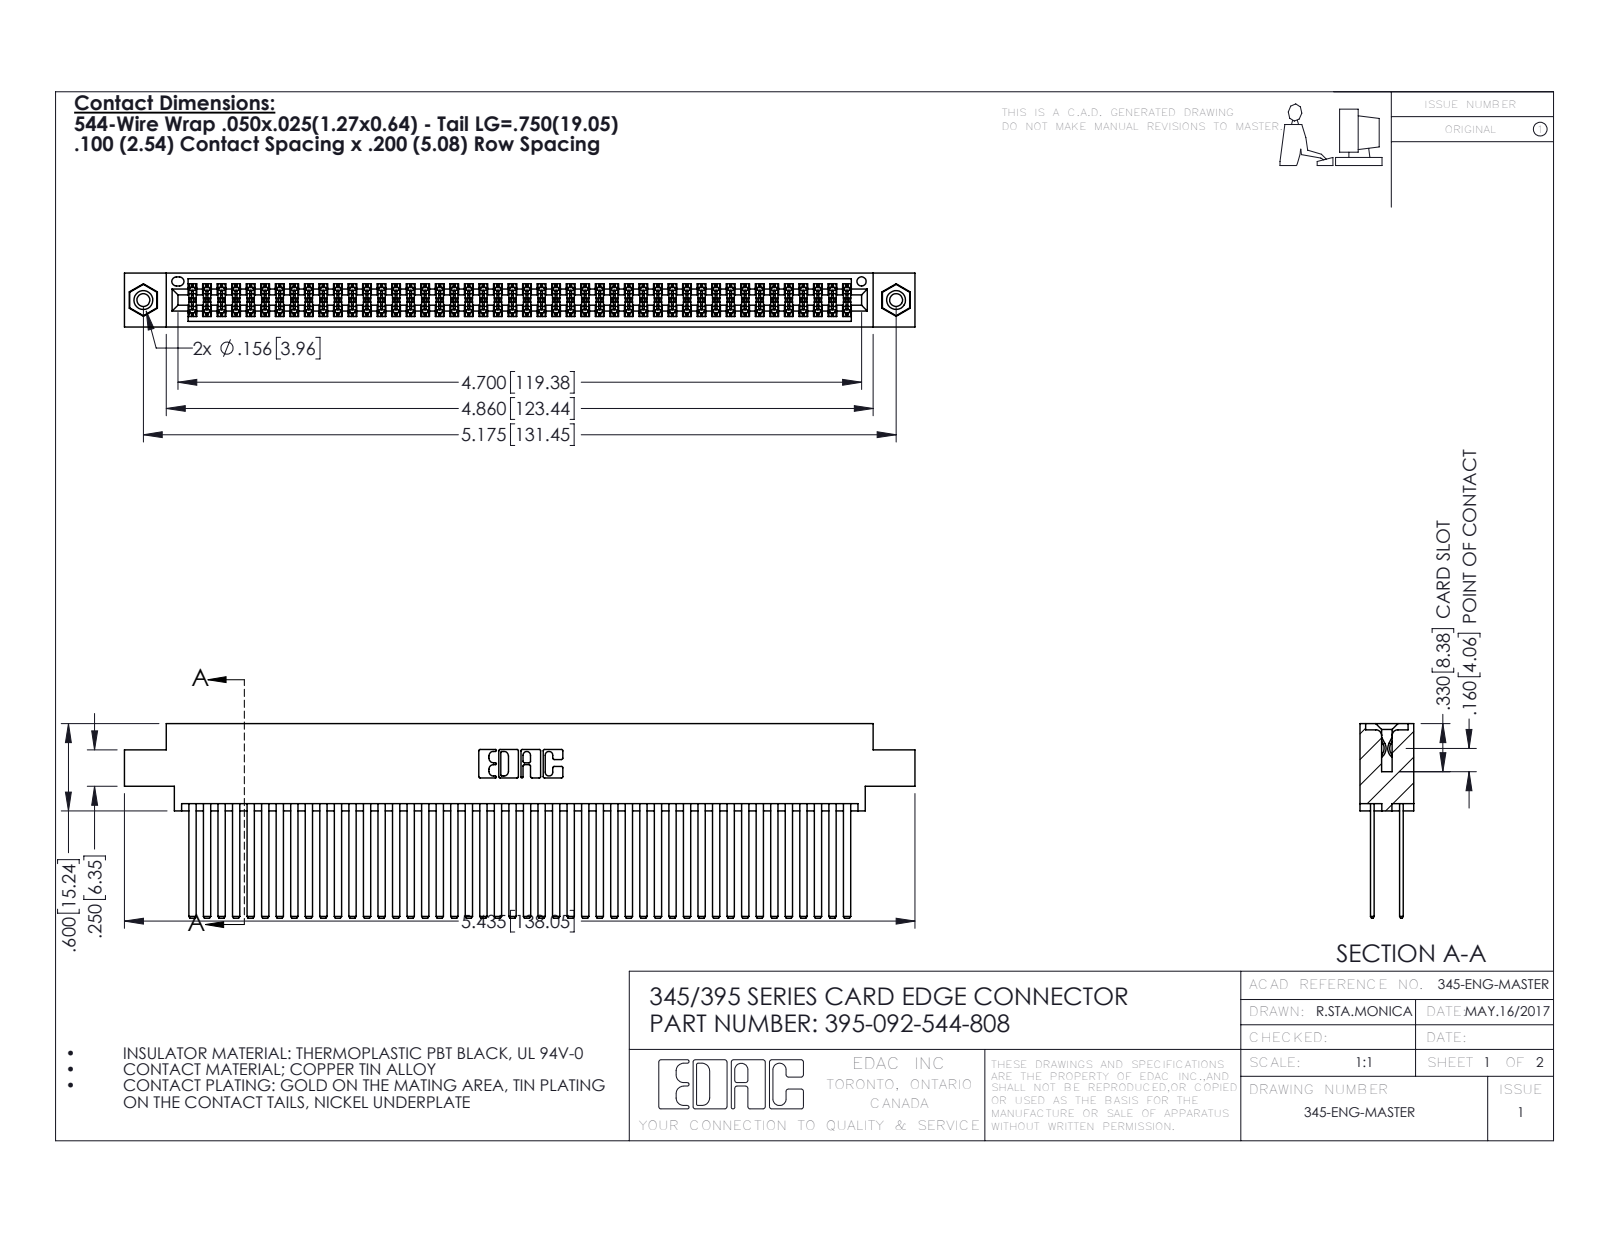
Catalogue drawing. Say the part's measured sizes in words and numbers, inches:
The part is named "395-092-544-808; 345-250-001_345-250-003-102; 345-292-001_345-293-144; 345 Part_0.170 Offset - 0.156 Dia-TI". Its 3-D file was written by "SolidWorks 2016 (CONFIG_CONTROL_DESIGN)". It is 95 solids with 4238 faces: 2784 planar, 1438 cylindrical and 16 other. Overall it measures 5.435 by 1.337 by 0.37 inches. Its volume is 0.892 cubic inches and its surface area 39.71 square inches. Round holes: 2 of diameter 0.089, 2 of diameter 0.125, 2 of diameter 0.156, 1 of diameter 0.064. Round bosses or shafts: 2 of diameter 0.155. Partial cylindrical surfaces (rounded edges, fillets, slot ends): 138 of radius 0.006, 22 of radius 0.01, 6 of radius 0.007, 6 of radius 0.031, 3 of radius 0.026, 2 of radius 0.014, 2 of radius 0.019, 2 of radius 0.022. The main face-to-face distances are 0.2, 0.025, 0.072, 0.098, 0.272, 0.298, 0.225, 0.175, 0.37, 0.15. The hole center spacings are 0.27, 4.939, 5.175.
